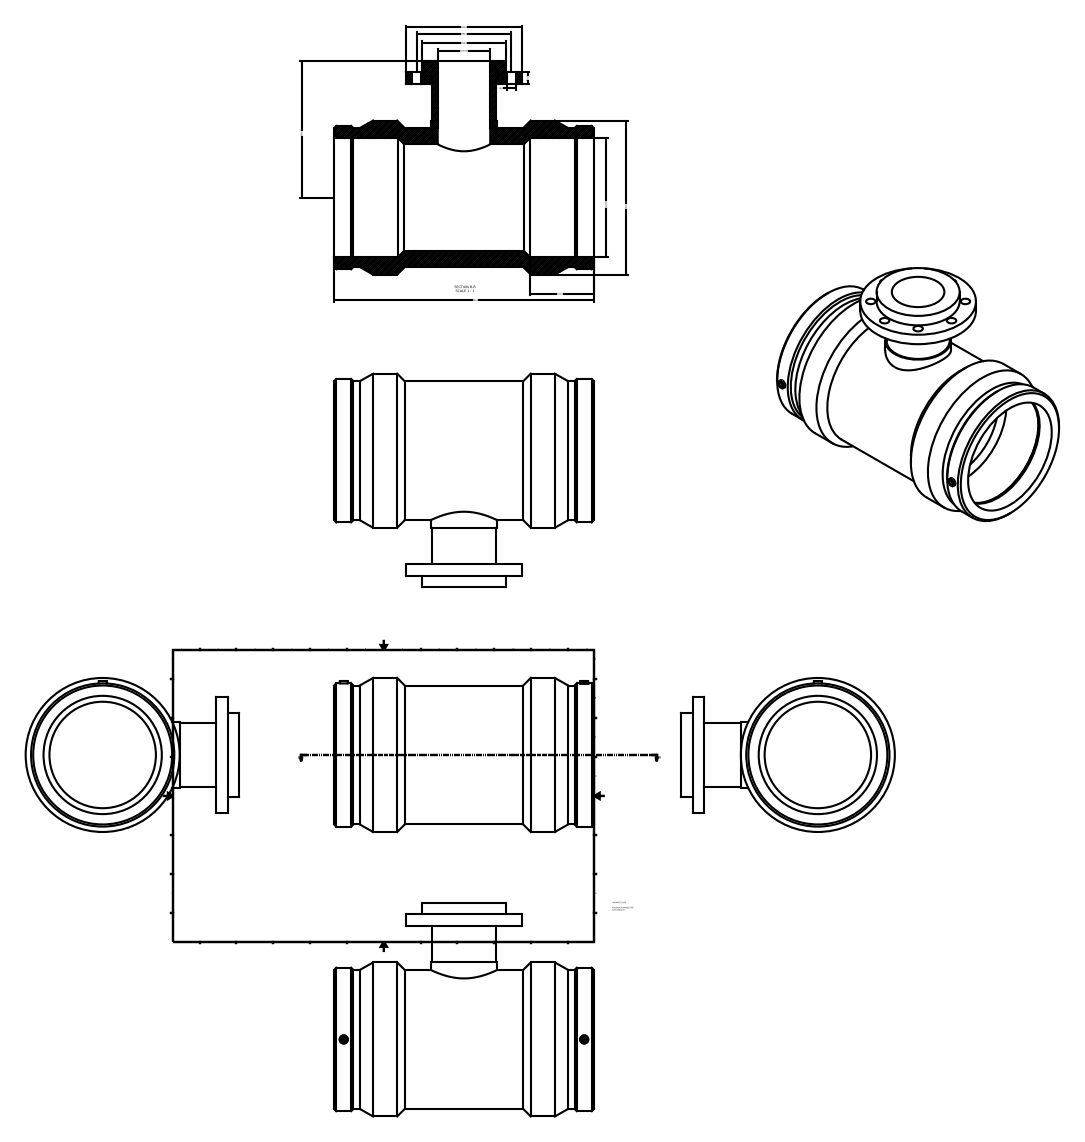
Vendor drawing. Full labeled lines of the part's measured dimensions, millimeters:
Part name (STEP PRODUCT): 499404225100
STEP written by: Autodesk Inventor 2015 (AUTOMOTIVE_DESIGN)
Units: millimetres
Bodies: 1 solid, 60 faces (14 planar, 30 cylindrical, 16 other)
Overall size (bounding box): 494 × 406.5 × 293
Volume: 12 010 000 mm³ · Surface area: 989 541 mm²
Round holes (diameter × count): ⌀18 ×8, ⌀10 ×2, ⌀100 ×1, ⌀130 ×1, ⌀202.5 ×1, ⌀225 ×1
Round bosses / shafts (diameter × count): ⌀4 ×2, ⌀293 ×1, ⌀272.49 ×1, ⌀264.32 ×1, ⌀263.7 ×1, ⌀220 ×1, ⌀158 ×1, ⌀125 ×1
Main face-to-face distances: 22, 494, 44, 36.04, 457.96, 113.5, 91.5, 69.5, 421.92, 14
Hole centre spacings: 68.88, 90, 127.28, 166.3, 180, 457.4
